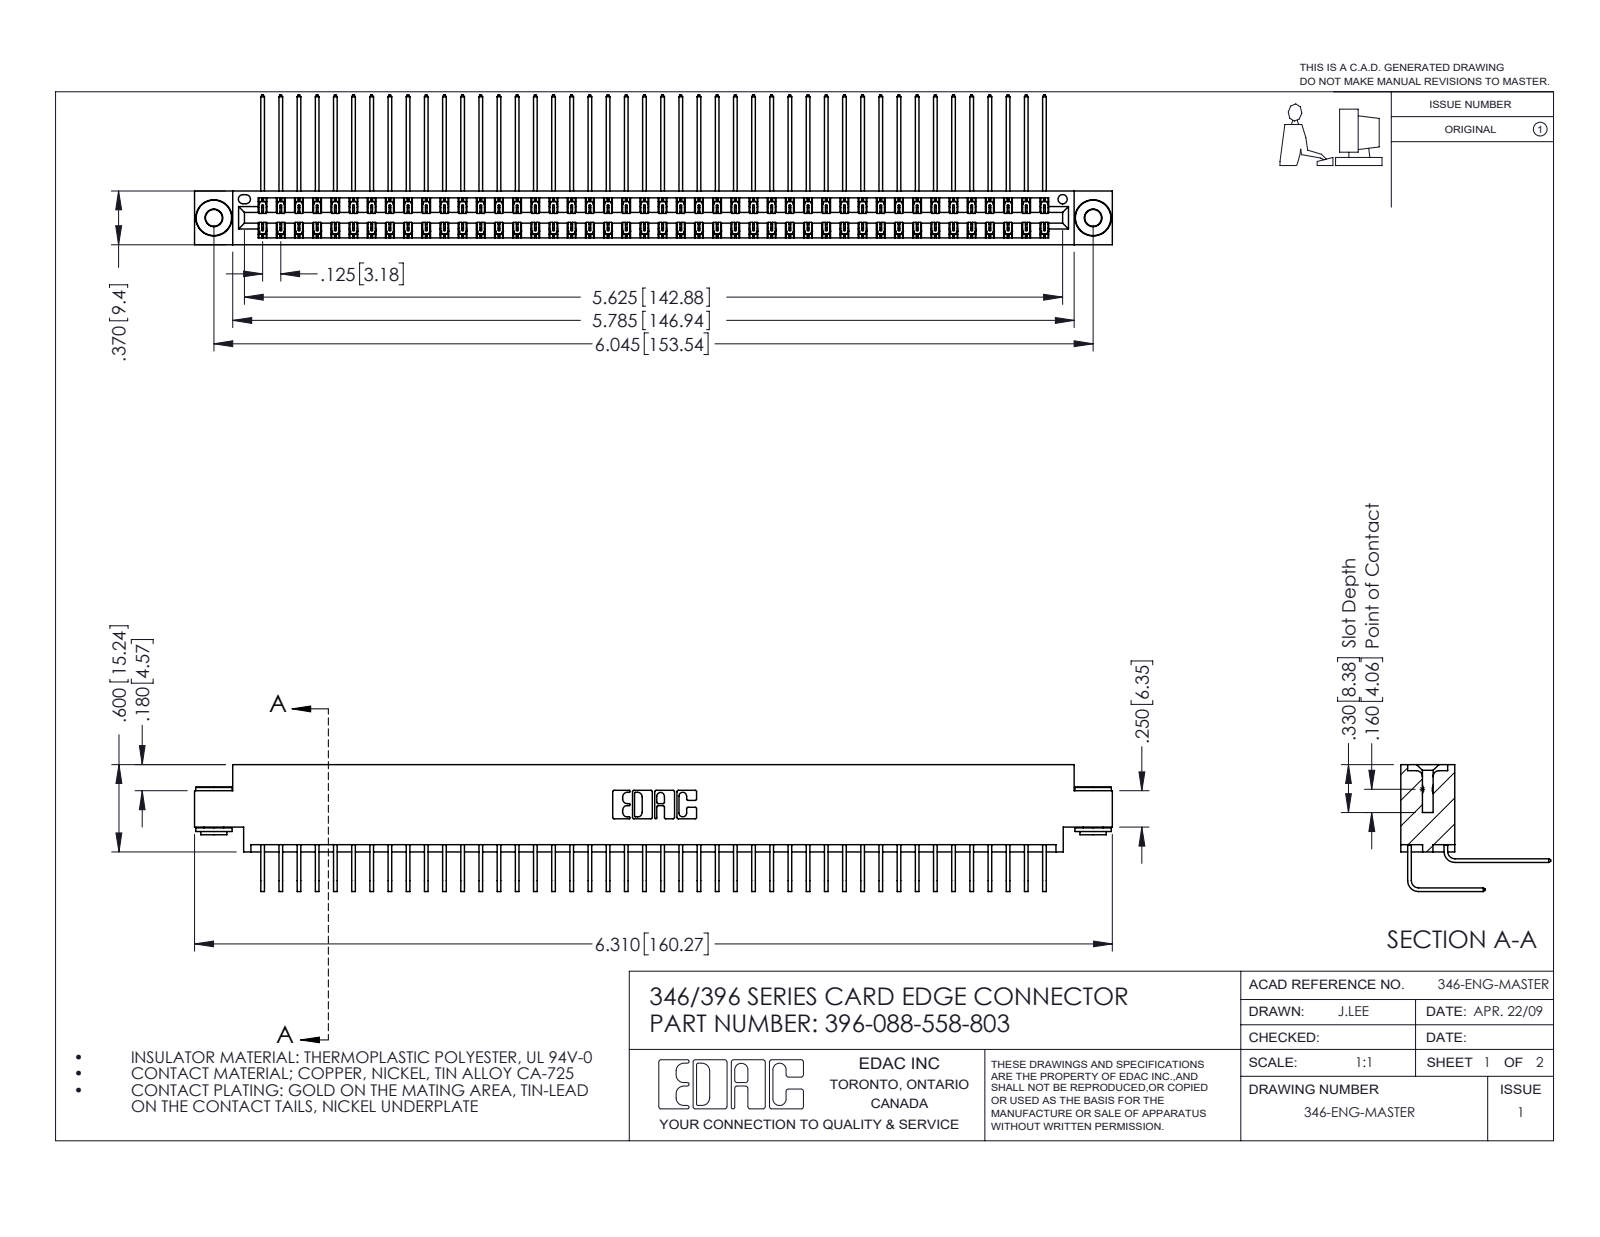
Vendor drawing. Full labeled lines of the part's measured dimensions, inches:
Part name (STEP PRODUCT): 345-250-002_345-250-002-102; 396-088-558-803; 346 Part_0.170 Offset - 0.156 Dia-TH; 345-292-001_558 559 Tail - 1 (+1 more)
STEP written by: SolidWorks 2016 (CONFIG_CONTROL_DESIGN)
Units: inches
Bodies: 91 solids, 4916 faces (3346 planar, 1562 cylindrical, 8 other)
Overall size (bounding box): 6.31 × 1.03 × 0.873
Volume: 0.977 in³ · Surface area: 38.56 in²
Round holes (diameter × count): ⌀0.116 ×2, ⌀0.156 ×2, ⌀0.064 ×1
Round bosses / shafts (diameter × count): ⌀0.25 ×2, ⌀0.18 ×2, ⌀0.136 ×2
Partial cylindrical surfaces — rounded edges, fillets, slot ends (radius × count): R0.006 ×132, R0.01 ×22, R0.007 ×6, R0.031 ×6, R0.026 ×3, R0.014 ×2, R0.022 ×2, R0.024 ×2
Main face-to-face distances: 0.322, 0.048, 0.025, 0.37, 0.25, 0.298, 0.072, 0.275, 0.148, 0.222
Hole centre spacings: 0.246, 5.836, 6.045
